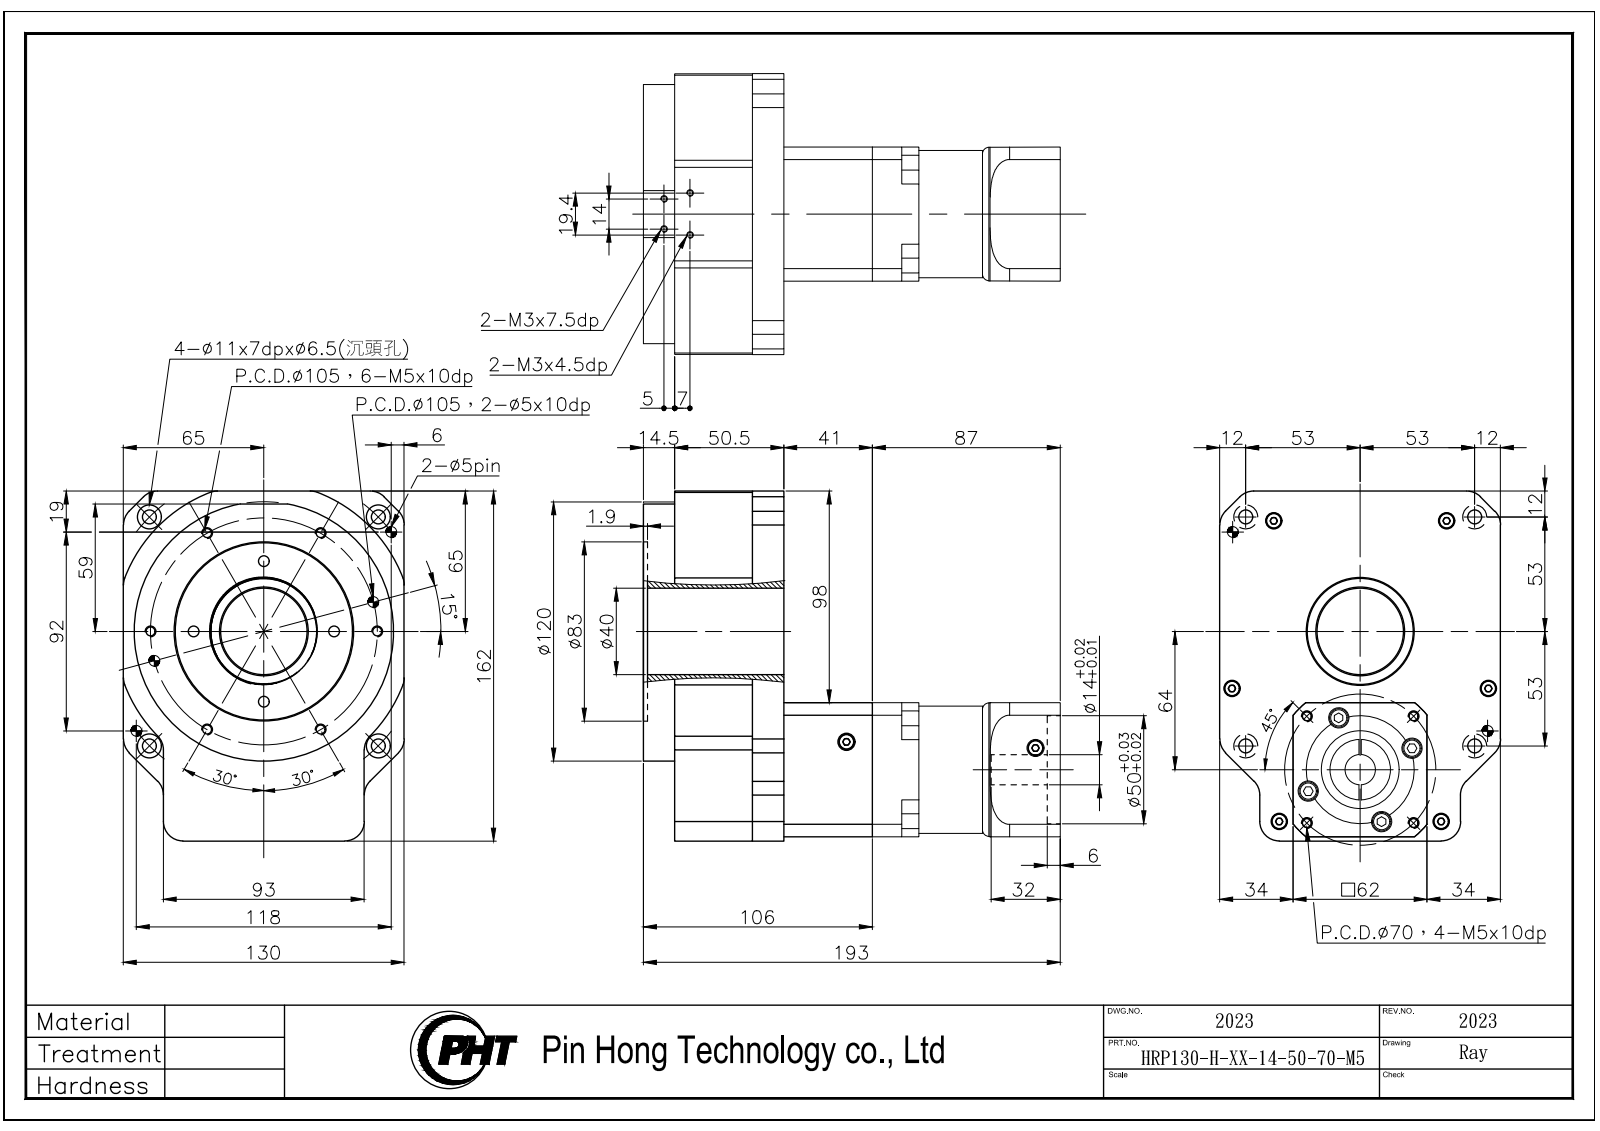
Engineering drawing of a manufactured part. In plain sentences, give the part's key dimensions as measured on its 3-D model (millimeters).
The part is named "HRP130-H-XX-14-50-70-M5_2023". Its 3-D file was written by "SolidWorks 2016 (CONFIG_CONTROL_DESIGN)". It is 2 solids with 599 faces: 251 planar, 276 cylindrical and 72 other. Overall it measures 193 by 162 by 130 millimeters. Its volume is 1 371 000 cubic millimeters and its surface area 151 174 square millimeters. Round holes: 16 of diameter 4.2, 8 of diameter 5, 8 of diameter 5.2, 8 of diameter 8, 6 of diameter 7.5, 4 of diameter 2.5, 4 of diameter 4.3, 4 of diameter 6.5, 4 of diameter 9.5, 4 of diameter 11, 2 of diameter 3.3, 2 of diameter 50. Round bosses or shafts: 10 of diameter 7, 4 of diameter 8.5, 1 of diameter 120, 1 of diameter 82, 1 of diameter 61.8, 1 of diameter 59, 1 of diameter 32, 1 of diameter 28. Partial cylindrical surfaces (rounded edges, fillets, slot ends): 20 of radius 9, 4 of radius 5, 2 of radius 2.5, 1 of radius 4, 1 of radius 34, 1 of radius 40, 1 of radius 69. The main face-to-face distances are 62, 50.5, 14.5, 65, 96, 41, 1.9, 63.1, 12.6, 91.5. The hole center spacings are 52.5, 5.42, 9.83, 14.82, 26, 30, 34.71, 35.
